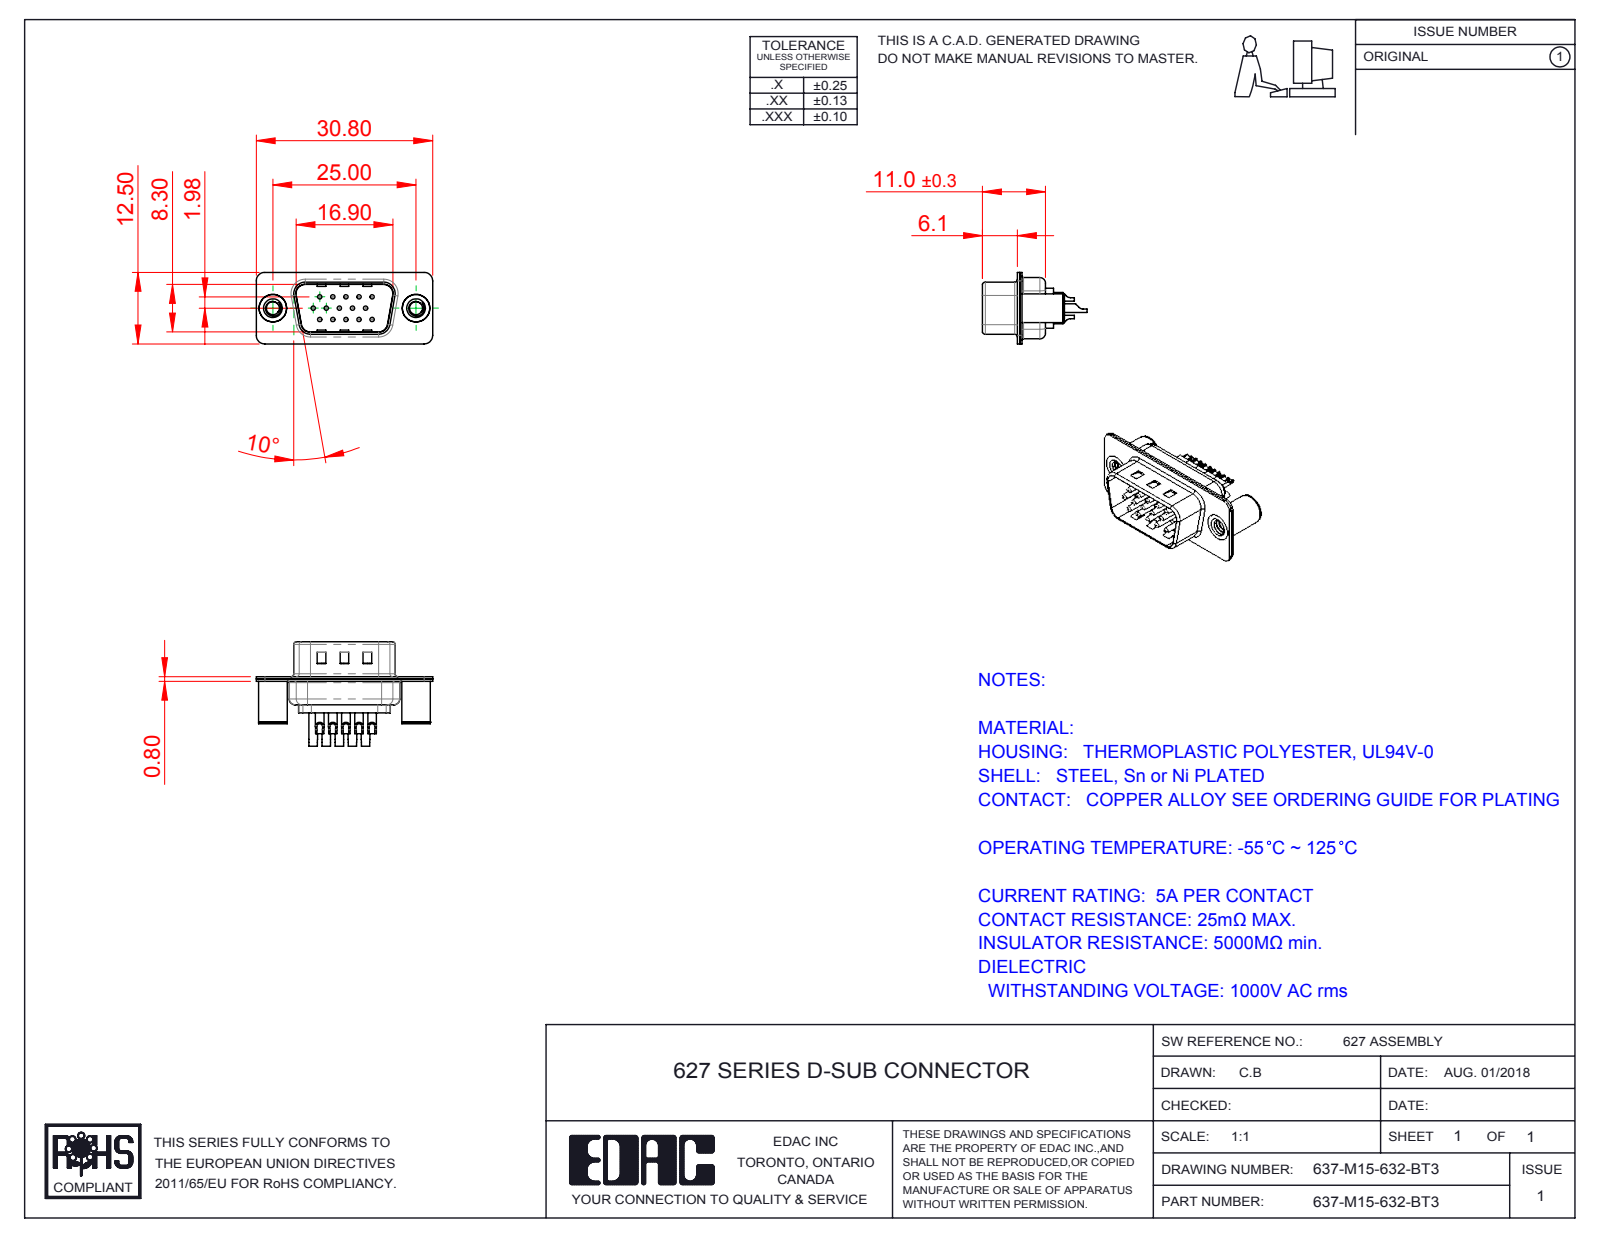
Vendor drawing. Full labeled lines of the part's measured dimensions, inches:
Part name (STEP PRODUCT): 637-M15-632-BT3; 637M 4-40 Threaded Board Spacer; 637M Shell Front_15 Contacts; 637M Contact Row 3_32 (+4 more)
STEP written by: SolidWorks 2016 (CONFIG_CONTROL_DESIGN)
Units: inches
Bodies: 20 solids, 893 faces (242 planar, 393 cylindrical, 258 other)
Overall size (bounding box): 1.213 × 0.719 × 0.492
Volume: 0.093 in³ · Surface area: 7.028 in²
Round holes (diameter × count): ⌀0.03 ×15, ⌀0.039 ×15, ⌀0.063 ×15, ⌀0.079 ×15, ⌀0.089 ×2, ⌀0.128 ×2, ⌀0.157 ×2, ⌀0.189 ×2
Round bosses / shafts (diameter × count): ⌀0.059 ×15, ⌀0.197 ×2, ⌀0.193 ×2
Partial cylindrical surfaces — rounded edges, fillets, slot ends (radius × count): R0.059 ×16, R0.079 ×12, R0.02 ×8, R0.063 ×8, R0.039 ×7, R0.01 ×4, R0.024 ×4, R0.026 ×4
Main face-to-face distances: 0.016, 0.031, 0.374, 0.358, 0.026, 0.343, 0.39, 0.03, 0.014, 0.047
Hole centre spacings: 0.156, 0.09, 0.09, 0.18, 0.238, 0.27, 0.312, 0.238
